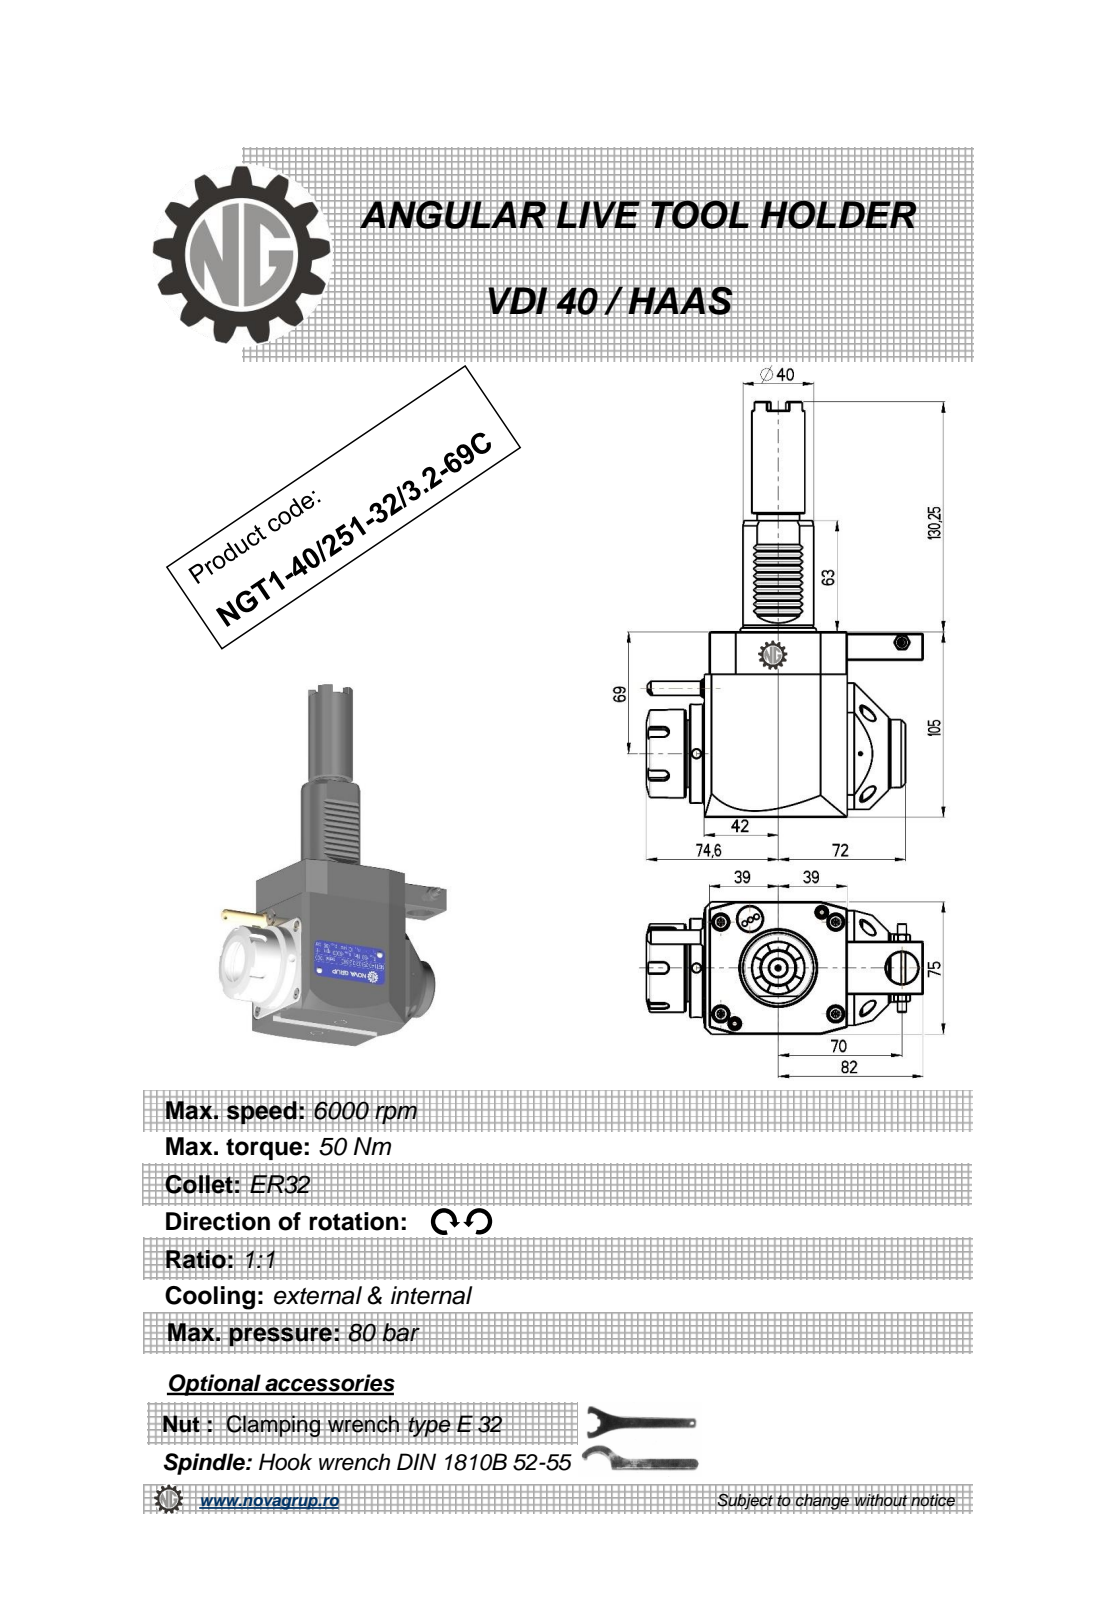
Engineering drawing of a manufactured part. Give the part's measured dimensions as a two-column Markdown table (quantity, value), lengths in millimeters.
| quantity | value |
| --- | --- |
| part name | NGT1_40_251_32_3_2_69C |
| STEP written by | PRO/ENGINEER BY PARAMETRIC TECHNOLOGY CORPORATION, 2010280 (CONFIG_CONTROL_DESIGN) |
| units | millimeters |
| bodies | 1 solid, 515 faces (228 planar, 113 cylindrical, 174 other) |
| overall size | 235.25 × 156.6 × 75 |
| volume | 890 776 mm³ |
| surface area | 79 810 mm² |
| round holes (diameter × count) | 3.3 × 4, 4.5 × 4, 8 × 4, 5 × 3, 3 × 1, 4.2 × 1, 9.5 × 1, 18 × 1, 20 × 1, 27 × 1 |
| round bosses / shafts (diameter × count) | 56 × 1, 50 × 1, 43 × 1, 40 × 1, 38.5 × 1, 30 × 1, 24 × 1, 10 × 1 |
| partial cylindrical surfaces (radius × count) | 0.26 × 12, 0.3 × 10, 0.2 × 6, 3 × 5, 0.5 × 1, 40 × 1 |
| main face-to-face distances | 75, 105, 81, 89, 1, 3, 2.8, 78, 80.8, 22.5 |
| hole center spacings | 32, 45.26, 44.98, 64.01, 87.12, 15.26, 30.11, 40.93 |
